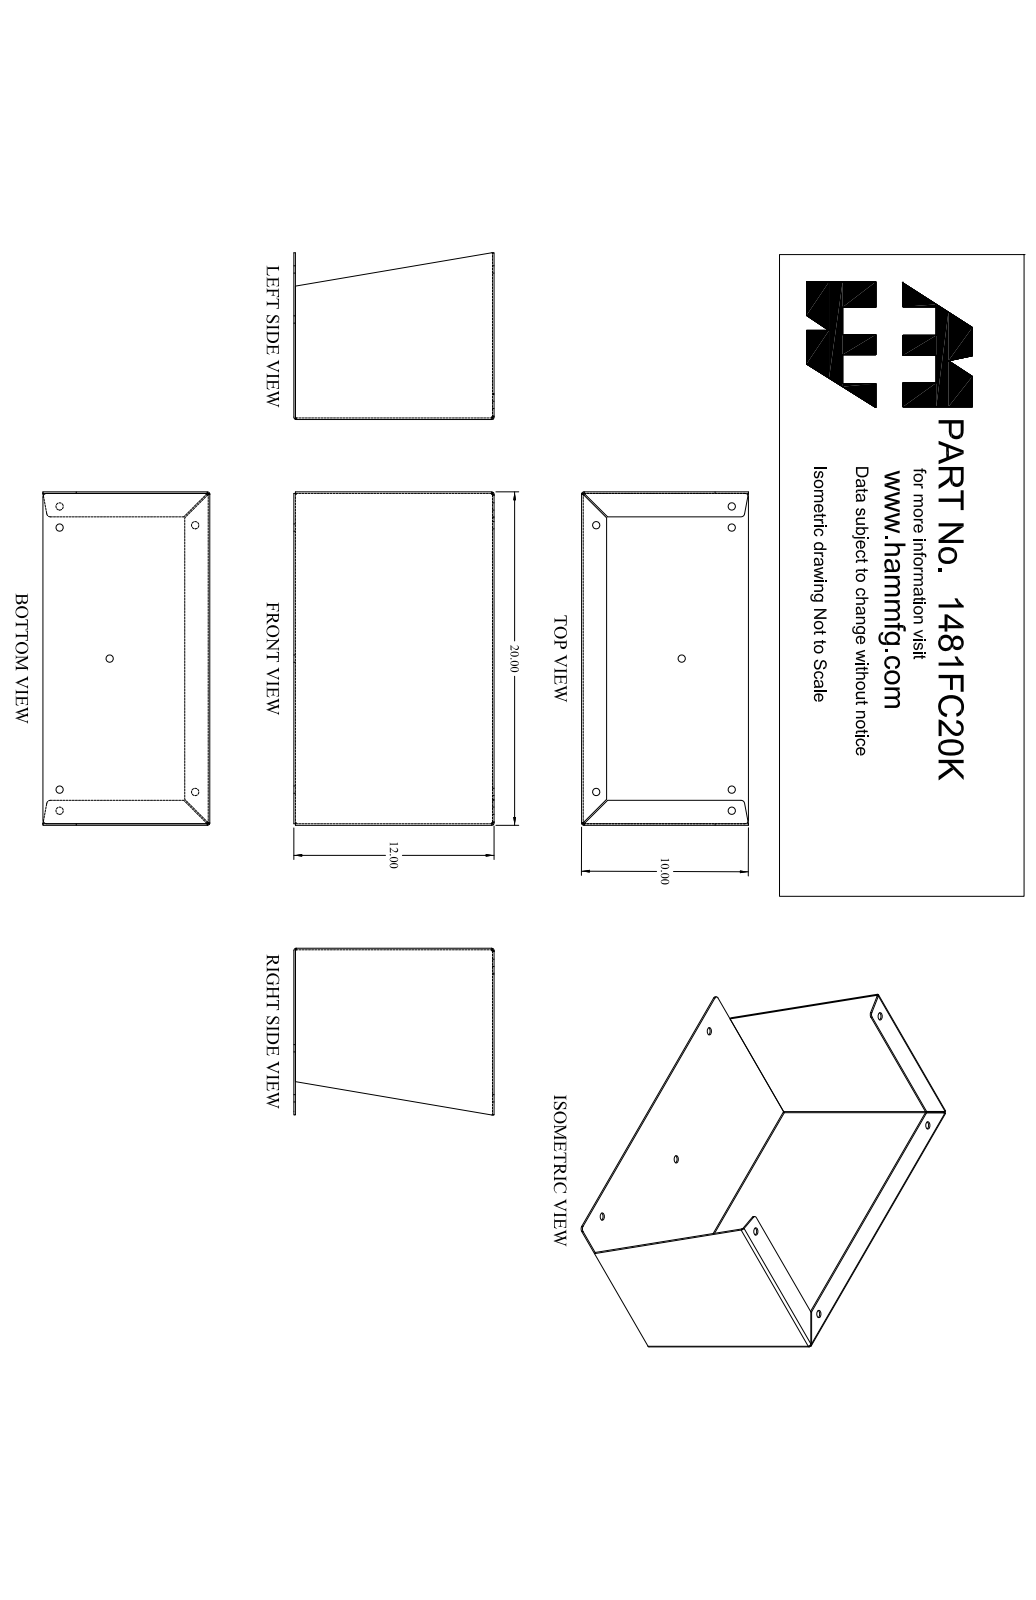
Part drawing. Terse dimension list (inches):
name: 1481FC20K_Default
written by: SolidWorks 2019 (CONFIG_CONTROL_DESIGN)
unit: in
bodies: 1 solid, 78 faces (42 planar, 30 cylindrical, 6 other)
size: 20 × 12 × 10
volume: 66.02 in³; area: 1 403 in²
holes: 7× ⌀0.437
rounds: 6× R0.048, 6× R0.143, 4× R0.22
face distances: 0.095, 19.905, 0.095, 20, 19.81, 11.81, 11.905, 11.905, 12, 1.405
hole spacings: 1.266, 8.126, 8.202, 8.412, 9.5, 9.606, 16.984, 17.819
